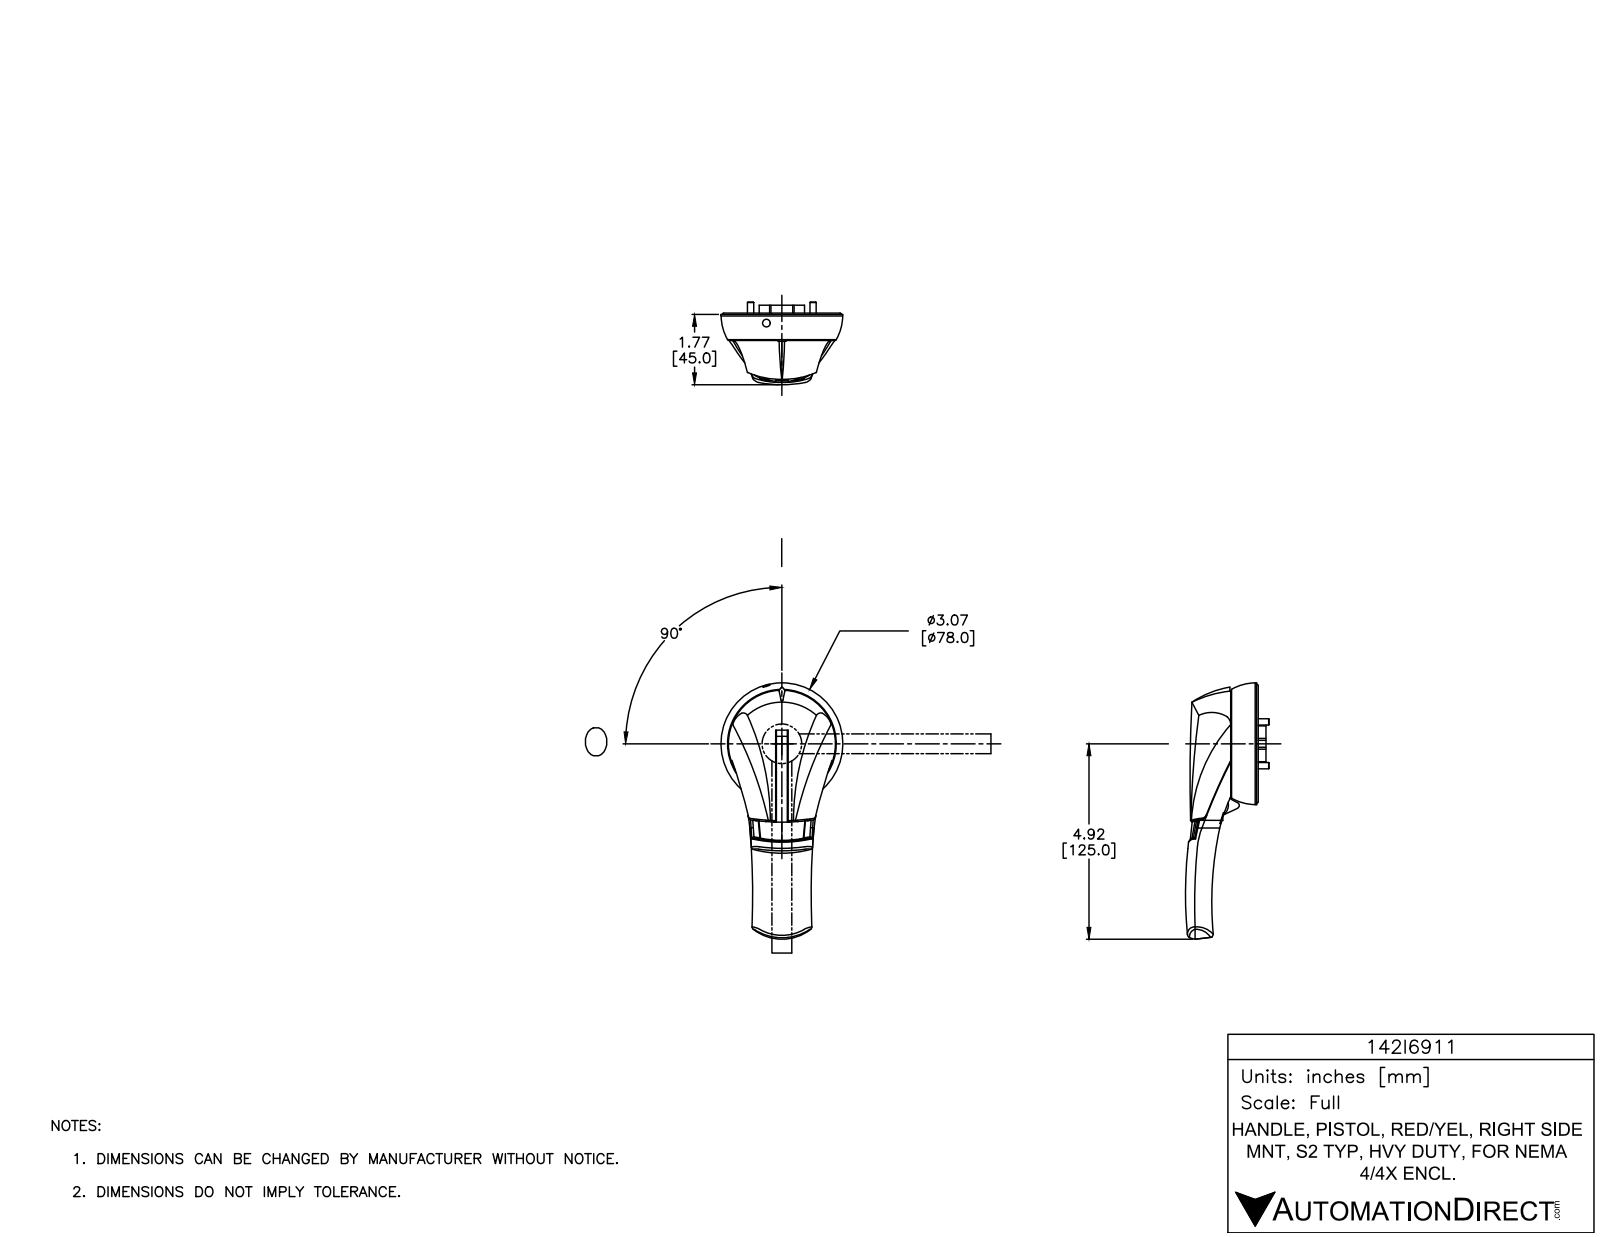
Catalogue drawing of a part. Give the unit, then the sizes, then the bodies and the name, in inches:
Units: inches
Overall size (bounding box): 6.458 × 3.07 × 2.079
Round holes (diameter × count): ⌀0.157 ×6, ⌀0.339 ×4, ⌀0.425 ×4, ⌀0.03 ×3, ⌀0.169 ×2, ⌀0.362 ×2, ⌀0.118 ×1, ⌀0.189 ×1, ⌀2.992 ×1
Round bosses / shafts (diameter × count): ⌀0.02 ×11, ⌀0.335 ×4, ⌀0.315 ×4, ⌀0.089 ×3, ⌀0.069 ×3, ⌀0.228 ×2, ⌀2.819 ×1, ⌀2.701 ×1
Partial cylindrical surfaces — rounded edges, fillets, slot ends (radius × count): R0.01 ×221, R0.015 ×20, R0.034 ×20, R0.03 ×15, R0.039 ×4, R0.025 ×3, R5.437 ×3, R0.079 ×2
Main face-to-face distances: 0.024, 0.701, 0.713, 0.689, 0.035, 0.102, 0.276, 0.173, 0.244, 0.047
Hole centre spacings: 0.961, 0.309, 0.669, 1.098, 1.102, 1.203, 1.575, 1.881
Volume: 9.514 in³ · Surface area: 87.32 in²
Bodies: 8 solids, 1516 faces (810 planar, 548 cylindrical, 158 other)
Part name (STEP PRODUCT): 142I6911
STEP written by: SolidWorks 2015 (AUTOMOTIVE_DESIGN)
